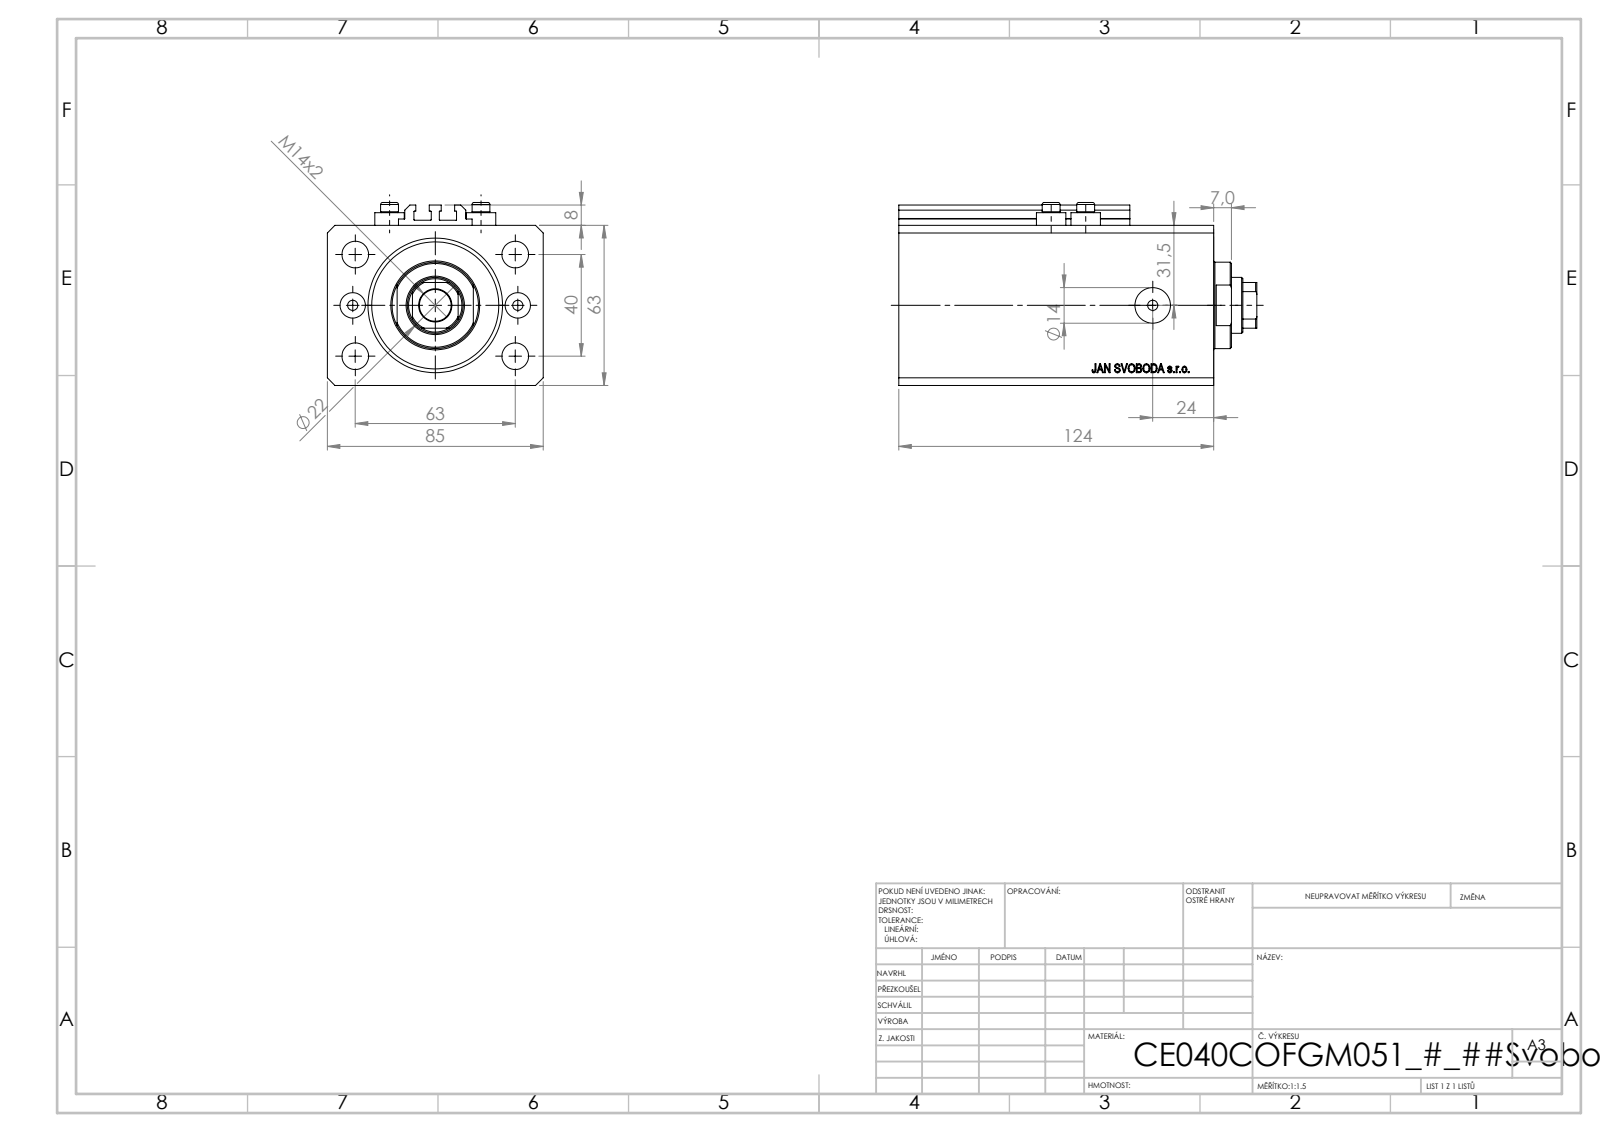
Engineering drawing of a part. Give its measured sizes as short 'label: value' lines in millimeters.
name: ALLEN BOLT V250CE; V250CE_VC_C; V250CE_C_VCP; V250CE_C_Body
written by: SolidWorks 2019 (CONFIG_CONTROL_DESIGN)
unit: mm
bodies: 8 solids, 1034 faces (504 planar, 86 cylindrical, 444 other)
size: 141 × 85 × 72
volume: 591 584 mm³; area: 114 404 mm²
holes: 8× ⌀4, 4× ⌀10.5, 2× ⌀10, 2× ⌀14, 1× ⌀12.5, 1× ⌀22, 1× ⌀40, 1× ⌀53
bosses: 4× ⌀11.6, 4× ⌀7, 1× ⌀34
rounds: 10× R0.2, 1× R10.5
face distances: 63, 85, 124, 17, 107, 11.4, 95.6, 112.6, 68, 2.5
hole spacings: 20.02, 37.31, 67.05, 13.6, 32.5, 36, 38.48, 40
